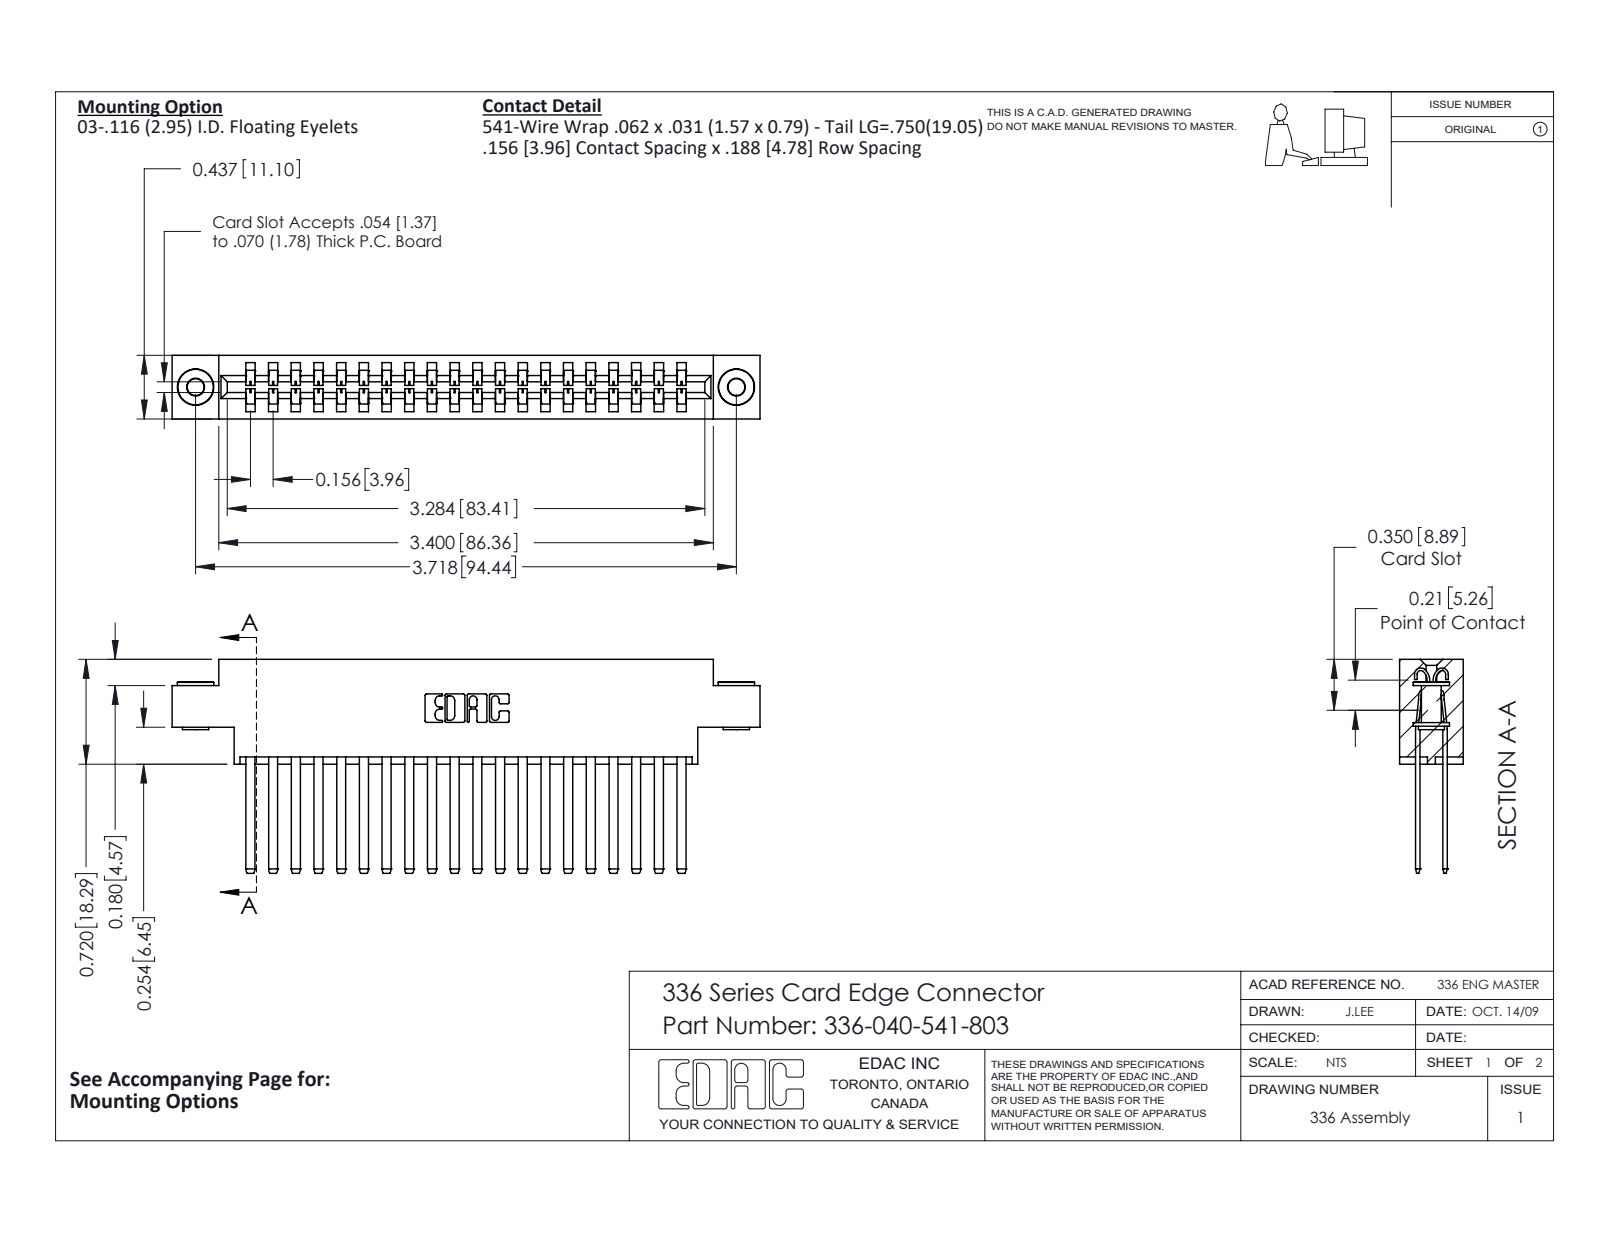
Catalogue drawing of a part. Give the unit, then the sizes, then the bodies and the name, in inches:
Units: inches
Overall size (bounding box): 4.041 × 1.47 × 0.437
Round holes (diameter × count): ⌀0.116 ×2, ⌀0.156 ×2
Round bosses / shafts (diameter × count): ⌀0.25 ×2, ⌀0.18 ×2, ⌀0.136 ×2
Partial cylindrical surfaces — rounded edges, fillets, slot ends (radius × count): R0.004 ×80, R0.056 ×40, R0.01 ×22, R0.007 ×6, R0.031 ×6, R0.022 ×4, R0.04 ×4, R0.026 ×3
Main face-to-face distances: 0.188, 0.031, 0.328, 0.14, 0.297, 0.109, 0.437, 0.033, 0.156, 0.181
Hole centre spacings: 3.718
Volume: 0.924 in³ · Surface area: 29.79 in²
Bodies: 43 solids, 1836 faces (1124 planar, 704 cylindrical, 8 other)
Part name (STEP PRODUCT): 336 Part_Offset - .156 Dia - TH; 336-040-541-803; 336-290-001_336-290-541; 345-250-002_345-250-002-102
STEP written by: SolidWorks 2020 (CONFIG_CONTROL_DESIGN)
